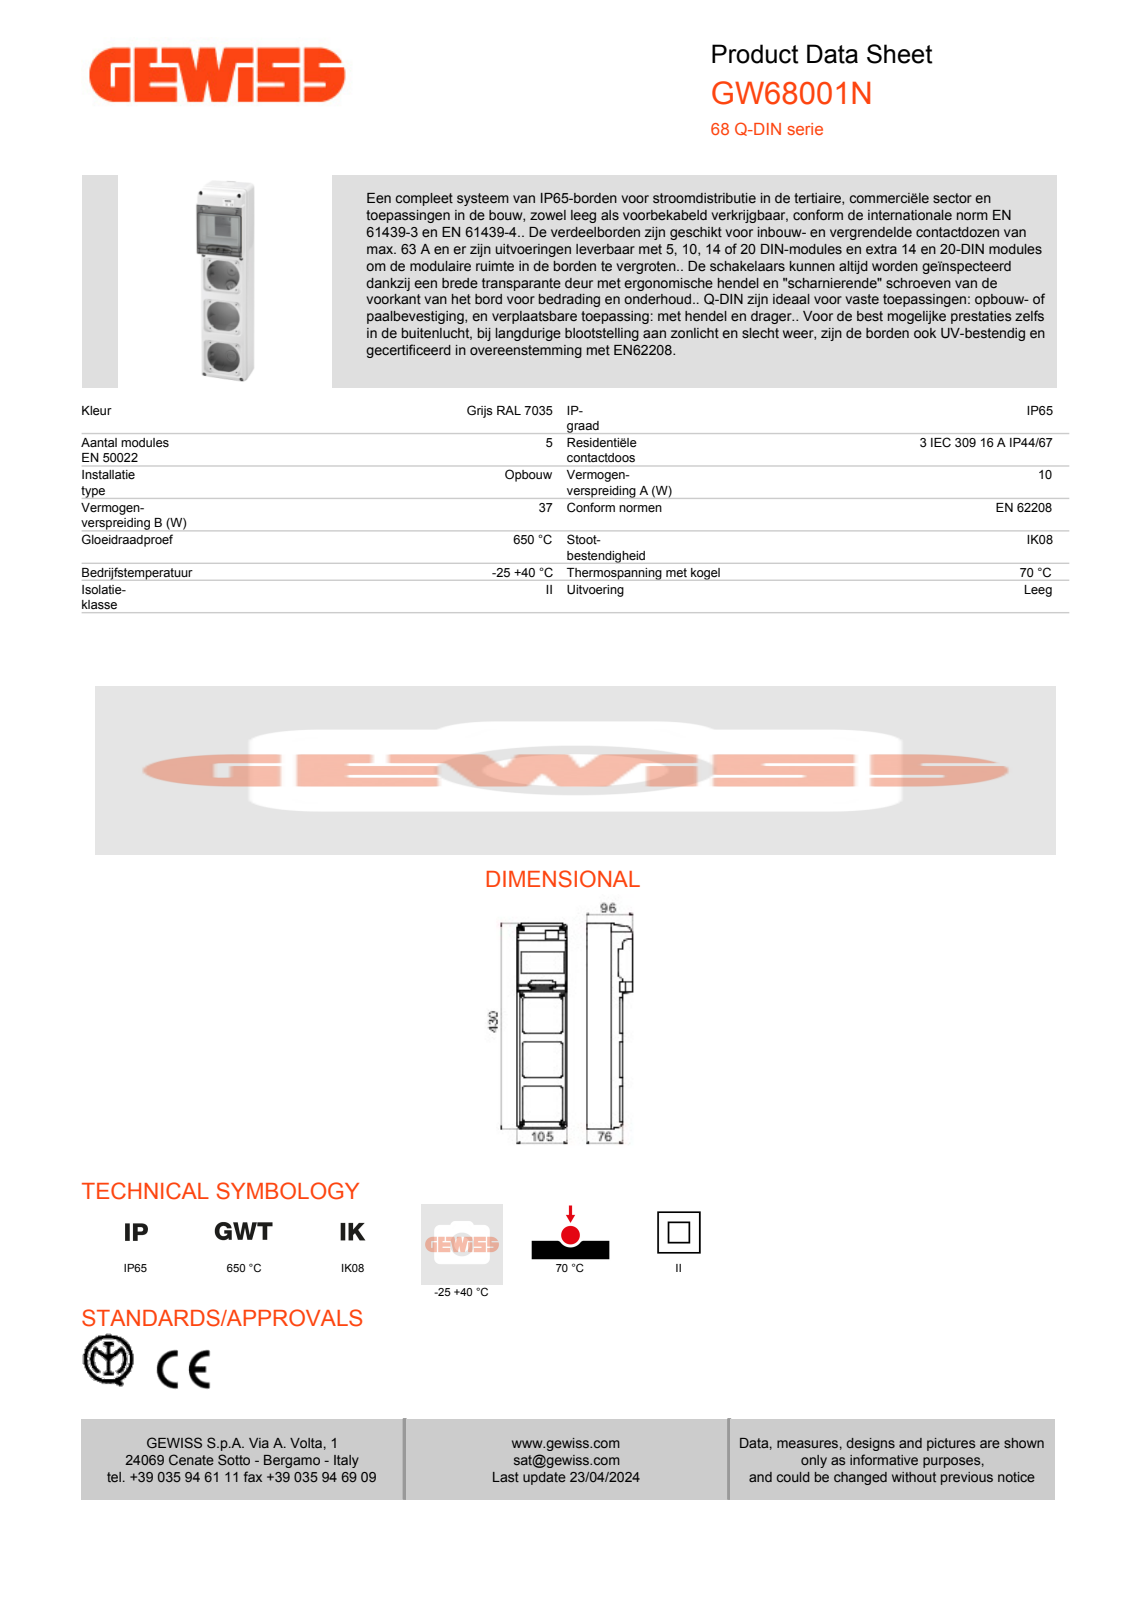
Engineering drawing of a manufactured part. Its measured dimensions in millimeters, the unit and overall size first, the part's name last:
Units: millimetres
Overall size (bounding box): 430 × 105 × 100.06
Partial cylindrical surfaces — rounded edges, fillets, slot ends (radius × count): R1.5 ×8, R2.5 ×8, R0.5 ×7, R1 ×7, R10 ×6, R33.5 ×6, R2 ×5, R1.3 ×4
Main face-to-face distances: 2.5, 105, 2.24, 97.09, 99.33, 20.5, 91.5, 94, 73.5, 71
Volume: 729 659 mm³ · Surface area: 359 620 mm²
Bodies: 2 solids, 687 faces (416 planar, 67 cylindrical, 204 other)
Part name (STEP PRODUCT): 55523971_FONDO_QDIN_5M_3PR_16A; 55523989E; GW68001N_ASM
STEP written by: CREO PARAMETRIC BY PTC INC, 2020354 (CONFIG_CONTROL_DESIGN)
